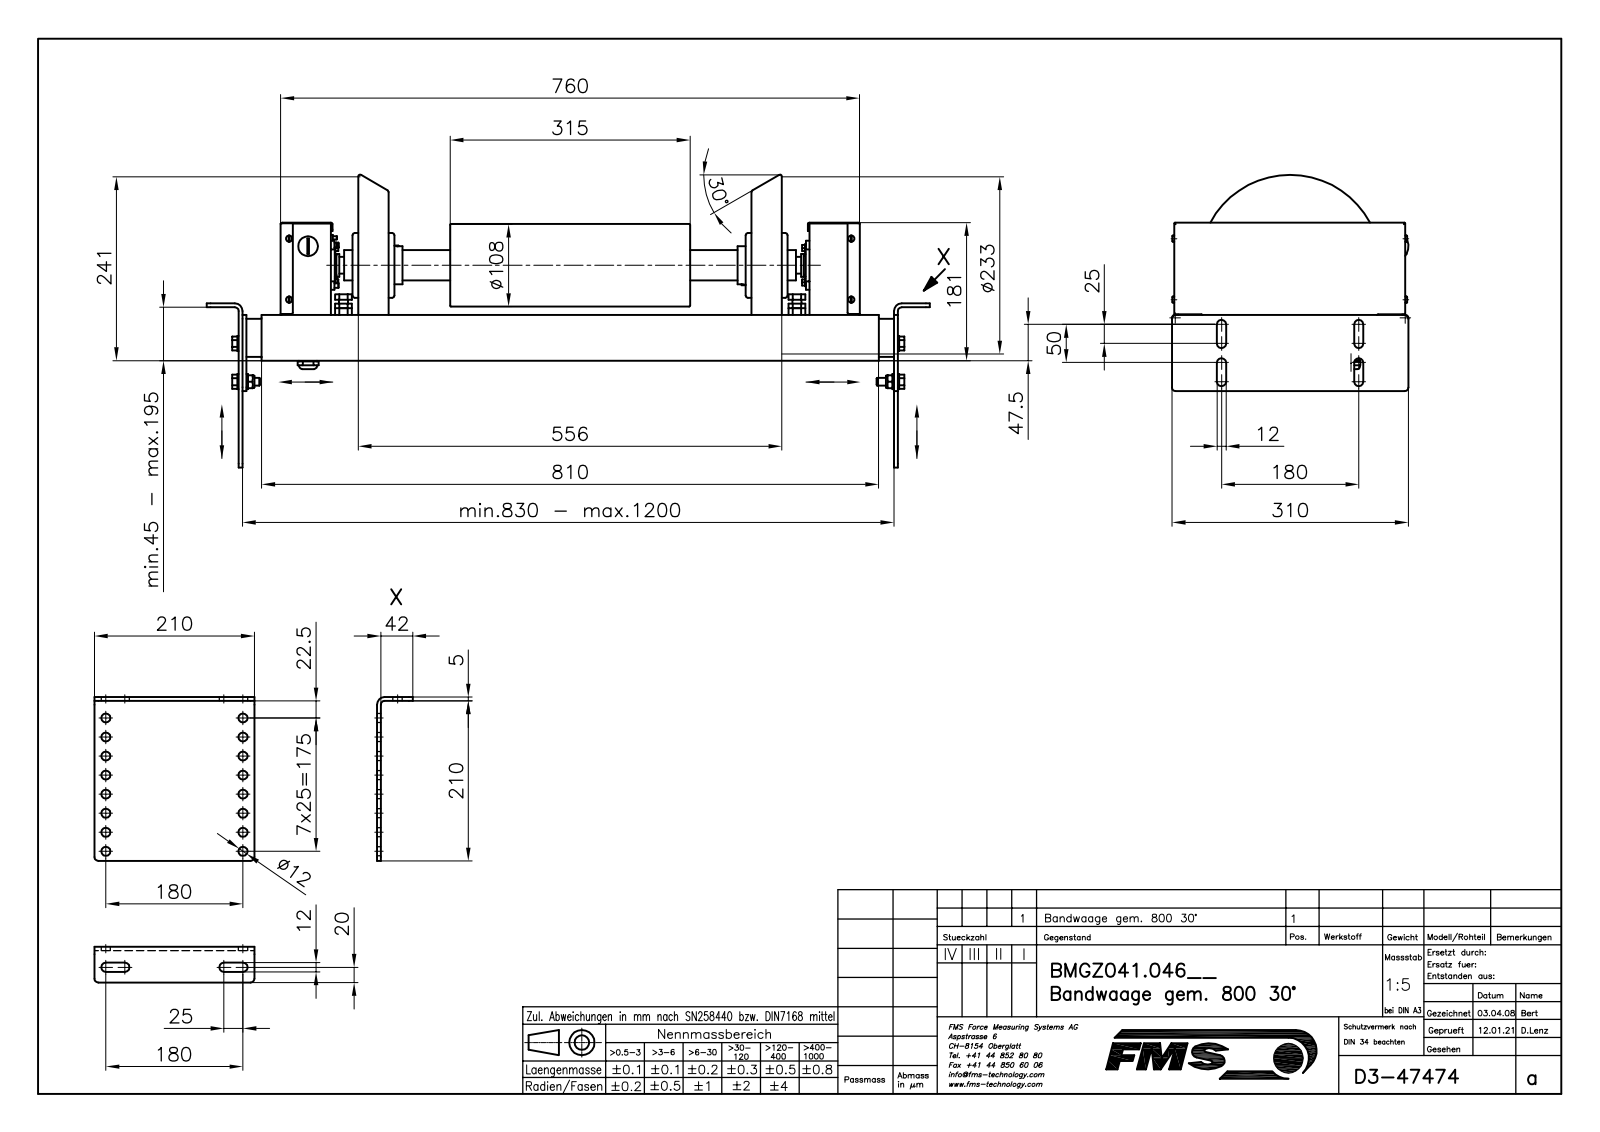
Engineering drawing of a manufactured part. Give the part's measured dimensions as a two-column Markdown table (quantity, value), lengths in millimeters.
| quantity | value |
| --- | --- |
| part name | B47474_STP; B50030; 6KT-SCHRAUBE_M12X30; ZYL_SCHR__M4X8 (+8 more) |
| STEP written by | Mechanical Desktop 2009 (CONFIG_CONTROL_DESIGN) |
| units | millimeters |
| bodies | 156 solids, 2658 faces (1351 planar, 944 cylindrical, 363 other) |
| overall size | 949 × 383.76 × 310.2 |
| volume | 8 132 000 mm³ |
| surface area | 2 686 000 mm² |
| round holes (diameter × count) | 12 × 17, 5 × 6, 3.5 × 4, 4.9 × 4, 6.4 × 4, 8.68 × 4, 8.75 × 4, 10 × 4, 10.5 × 4, 10.68 × 4, 14.8 × 4, 6 × 3 |
| round bosses / shafts (diameter × count) | 12 × 11, 8.2 × 8, 4.2 × 8, 20 × 6, 10 × 6, 5 × 5, 16 × 4, 11.1 × 4 |
| partial cylindrical surfaces (radius × count) | 2 × 34, 1 × 24, 4 × 16, 5 × 16, 6 × 14, 3.5 × 8, 2.25 × 6, 0.5 × 4 |
| main face-to-face distances | 4, 5, 1, 51, 36, 270, 46, 50, 3, 56 |
| hole center spacings | 25, 181.73, 50, 186.82, 75, 195, 100, 180 |
